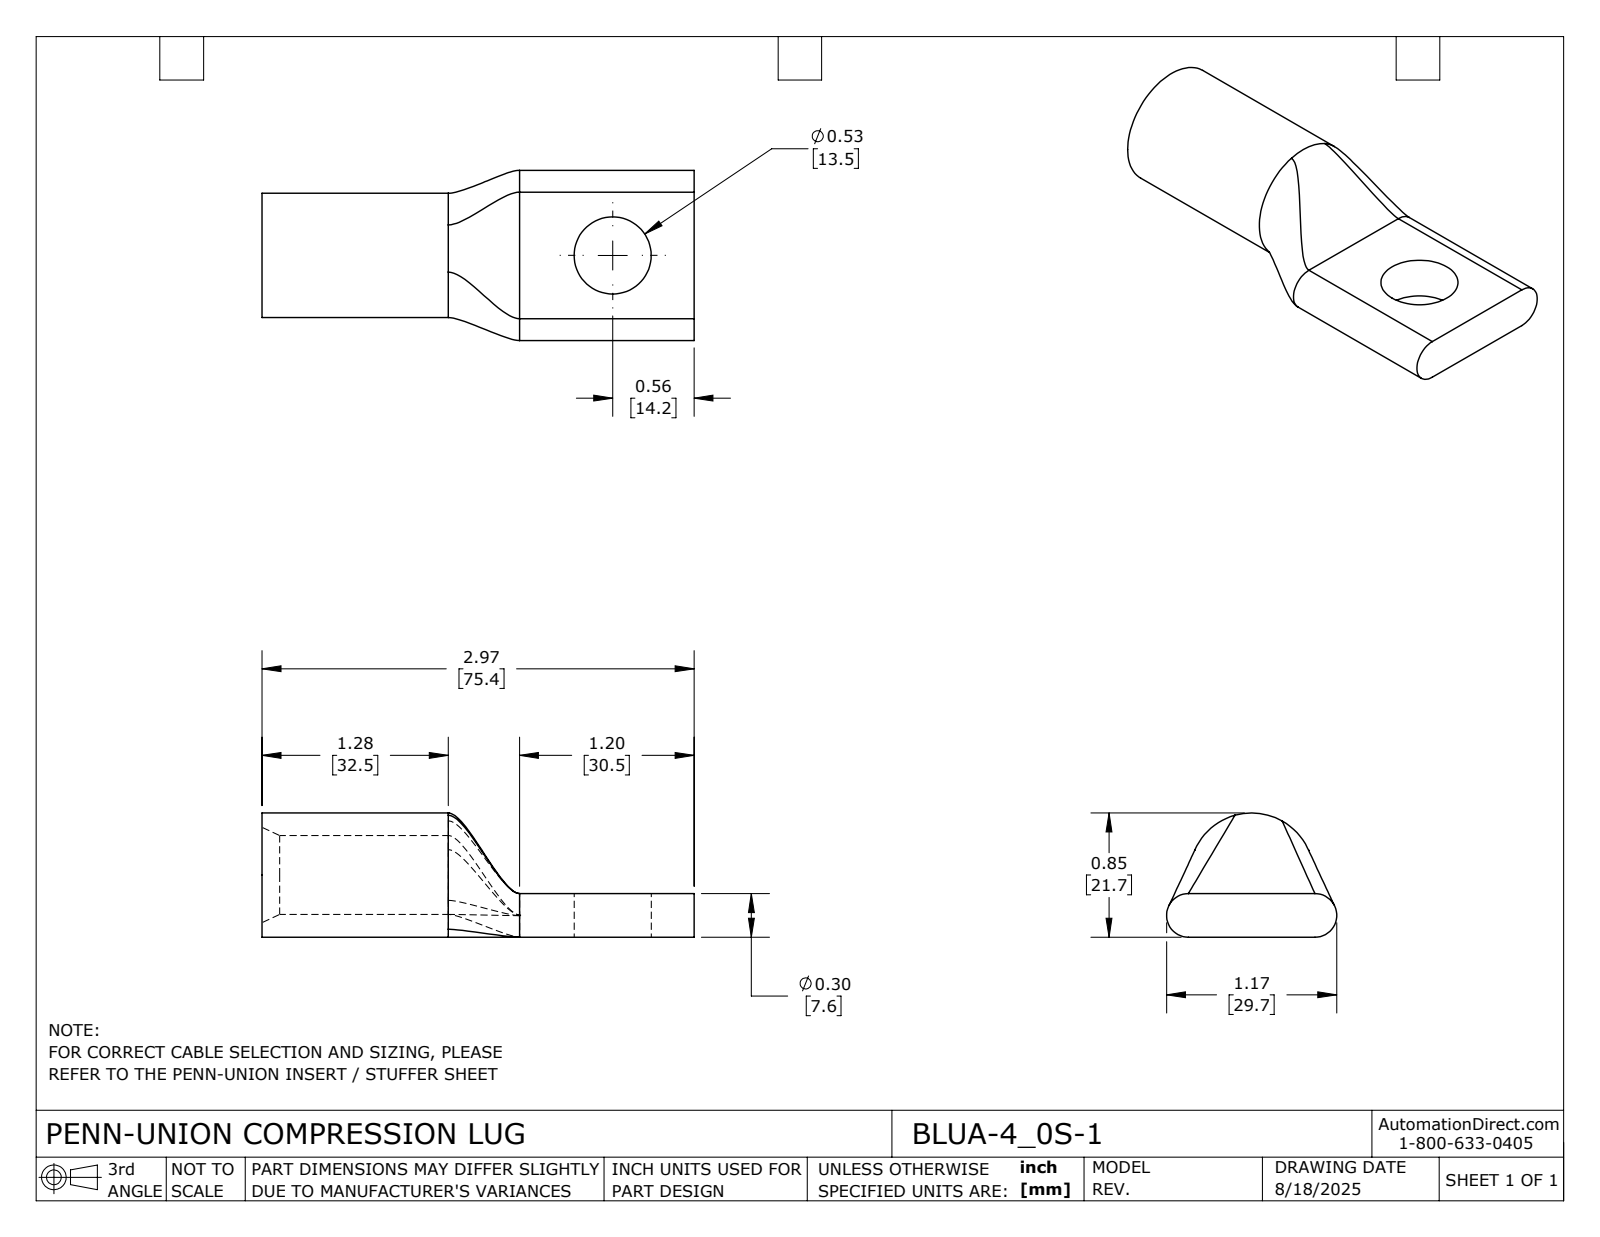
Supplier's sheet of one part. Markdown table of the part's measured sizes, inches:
| quantity | value |
| --- | --- |
| part name | BLUA-4_0S-1 |
| STEP written by | SolidWorks 2024 (CONFIG_CONTROL_DESIGN) |
| units | inches |
| bodies | 1 solid, 24 faces (5 planar, 9 cylindrical, 10 other) |
| overall size | 2.97 × 1.17 × 0.854 |
| volume | 0.927 in³ |
| surface area | 12.02 in² |
| round holes (diameter × count) | 0.53 × 1, 0.542 × 1 |
| round bosses / shafts (diameter × count) | 0.854 × 1 |
| partial cylindrical surfaces (radius × count) | 0.15 × 2 |
| main face-to-face distances | 0.3, 2.97, 1.77, 1.2 |
